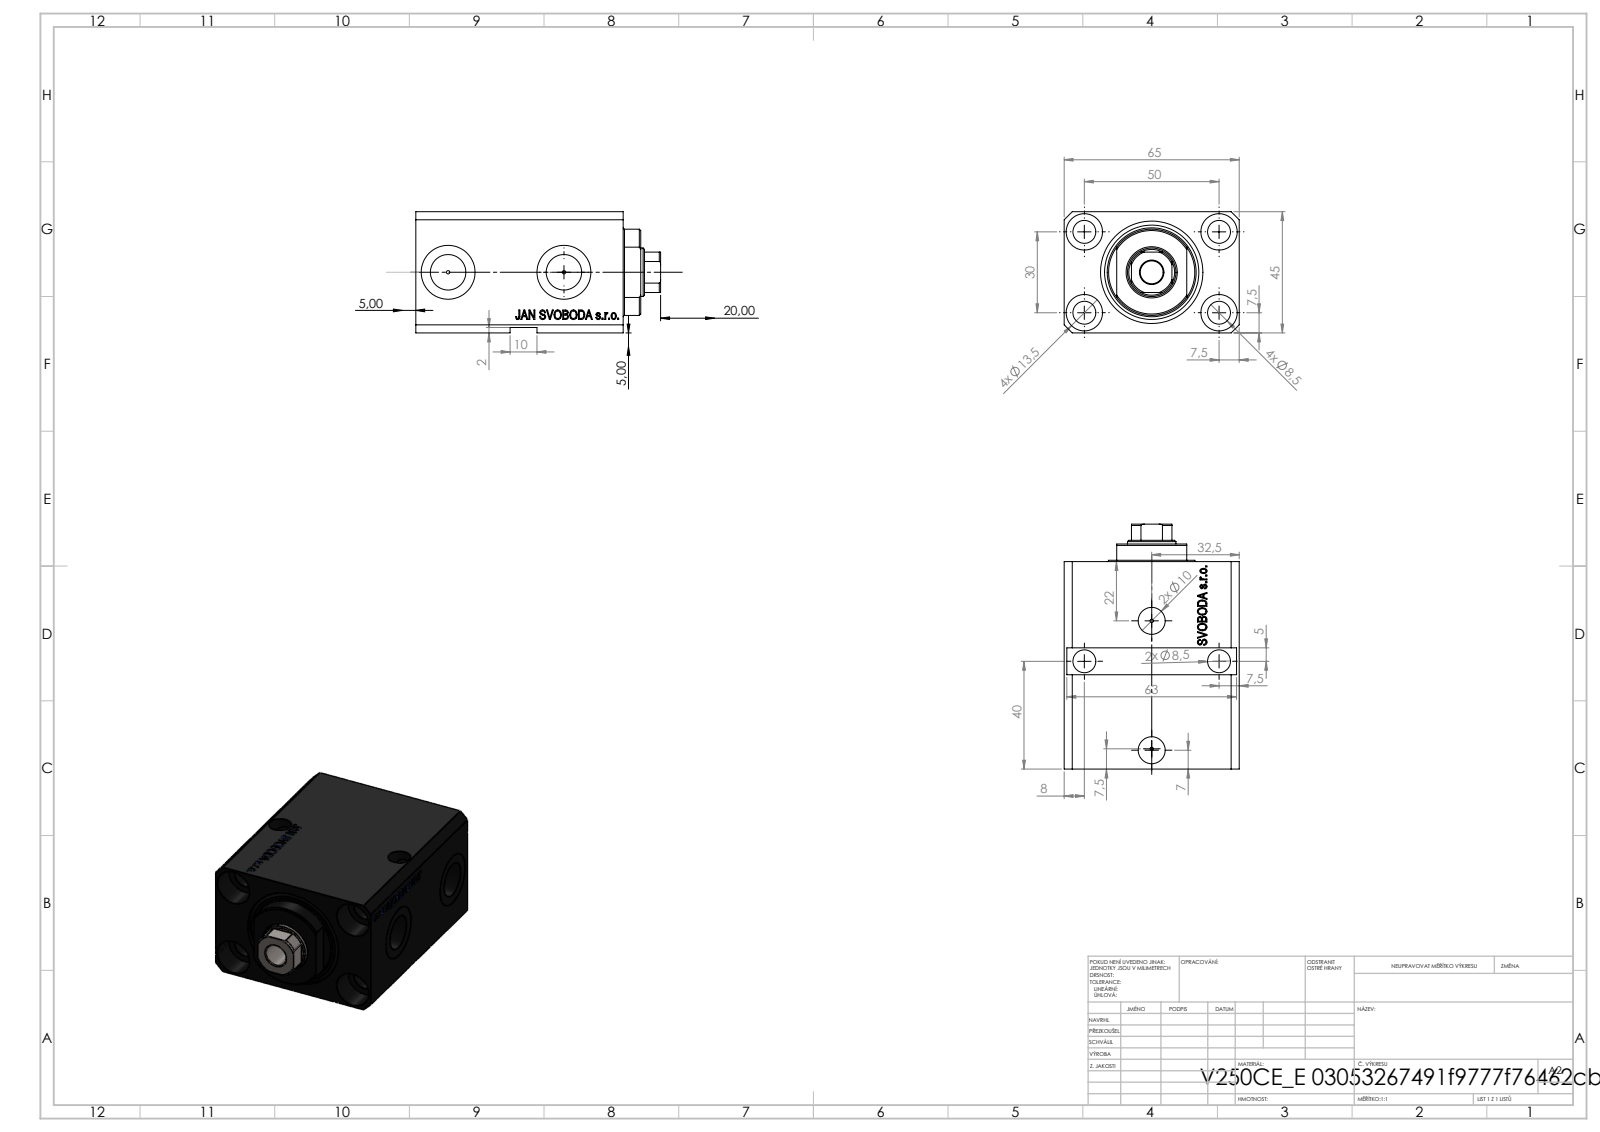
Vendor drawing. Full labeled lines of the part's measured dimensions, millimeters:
Part name (STEP PRODUCT): V250CE_VC_E; V250CE_E_Body; V250CE_C_VCP
STEP written by: SolidWorks 2019 (CONFIG_CONTROL_DESIGN)
Units: millimetres
Bodies: 3 solids, 913 faces (439 planar, 96 cylindrical, 378 other)
Overall size (bounding box): 91 × 65 × 45
Volume: 188 098 mm³ · Surface area: 53 396 mm²
Round holes (diameter × count): ⌀8.5 ×7, ⌀1.25 ×4, ⌀13.5 ×4, ⌀10 ×2, ⌀13.16 ×2, ⌀20 ×2, ⌀18 ×1, ⌀25 ×1, ⌀38 ×1
Partial cylindrical surfaces — rounded edges, fillets, slot ends (radius × count): R8.5 ×1, R16 ×1
Main face-to-face distances: 45, 65, 63, 14, 77, 6.9, 56.1, 70.1, 43, 64.9
Hole centre spacings: 29.15, 50, 30, 40.98, 41.4, 58.31, 0.53, 43
